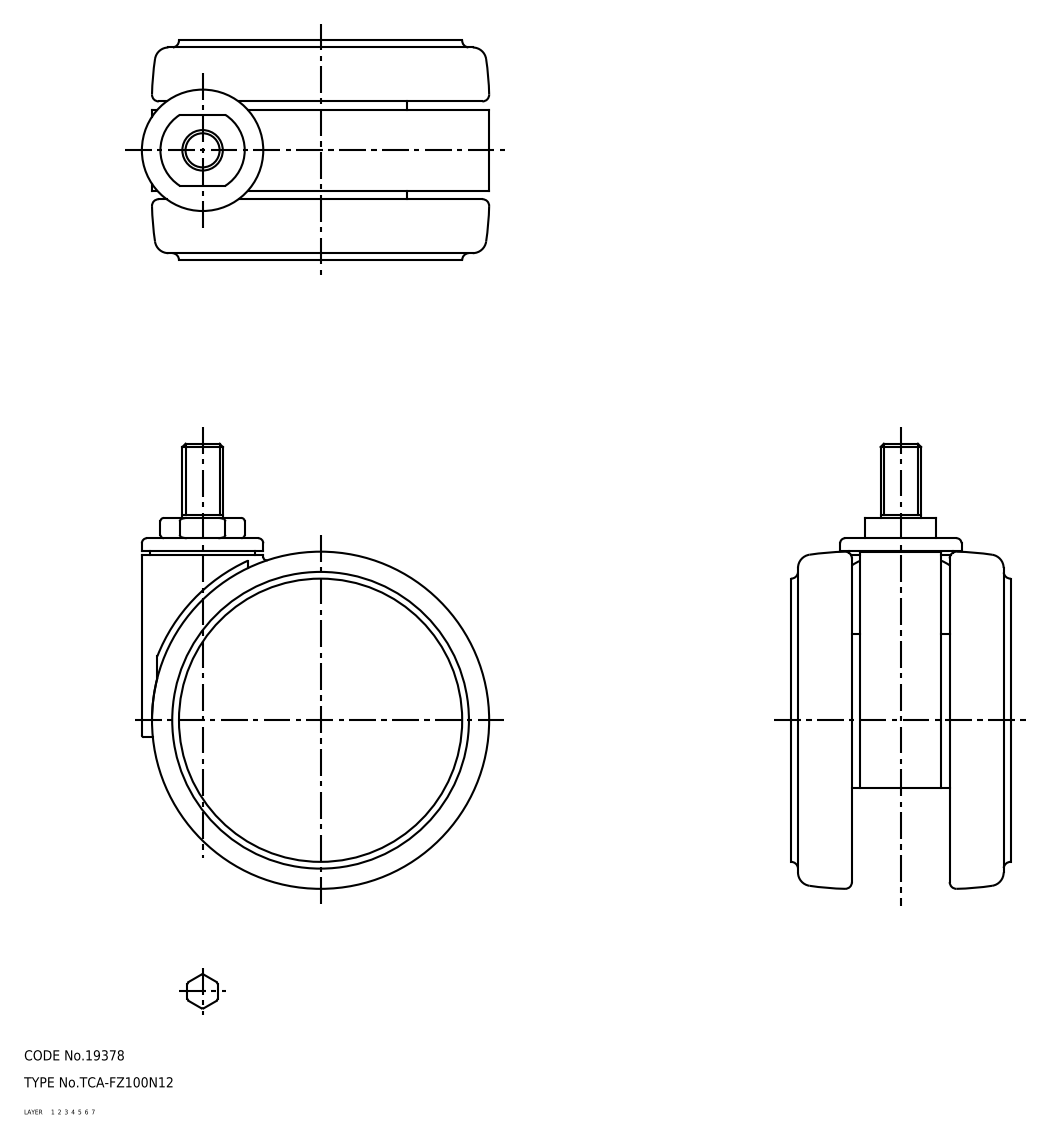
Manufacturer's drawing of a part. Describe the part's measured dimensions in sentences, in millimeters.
The part is named "TCA-FZ100N12; caster". Its 3-D file was written by "SolidWorks 2015 (AUTOMOTIVE_DESIGN)". It is 1 solid with 2344 faces: 792 planar, 1084 cylindrical and 468 other. Overall it measures 132 by 103 by 65.2 millimeters. Its volume is 296 746 cubic millimeters and its surface area 122 893 square millimeters. Round holes: 1 of diameter 9.1, 1 of diameter 10, 1 of diameter 10.1, 1 of diameter 10.5, 1 of diameter 12, 1 of diameter 15, 1 of diameter 15.2, 1 of diameter 15.8, 1 of diameter 19.2, 1 of diameter 26, 1 of diameter 28.2, 1 of diameter 30. Round bosses or shafts: 1 of diameter 87.8, 1 of diameter 36, 1 of diameter 31, 1 of diameter 27.9, 1 of diameter 27.6, 1 of diameter 20, 1 of diameter 19, 1 of diameter 18. Partial cylindrical surfaces (rounded edges, fillets, slot ends): 200 of radius 0.5, 160 of radius 1.2, 81 of radius 1, 16 of radius 0.2, 13 of radius 2, 12 of radius 0.3, 8 of radius 1.5, 6 of radius 0.8. The main face-to-face distances are 1.8, 61.6, 63.4, 3.6, 59.8, 14.5, 16.3, 13.25, 18.1, 47.1.
